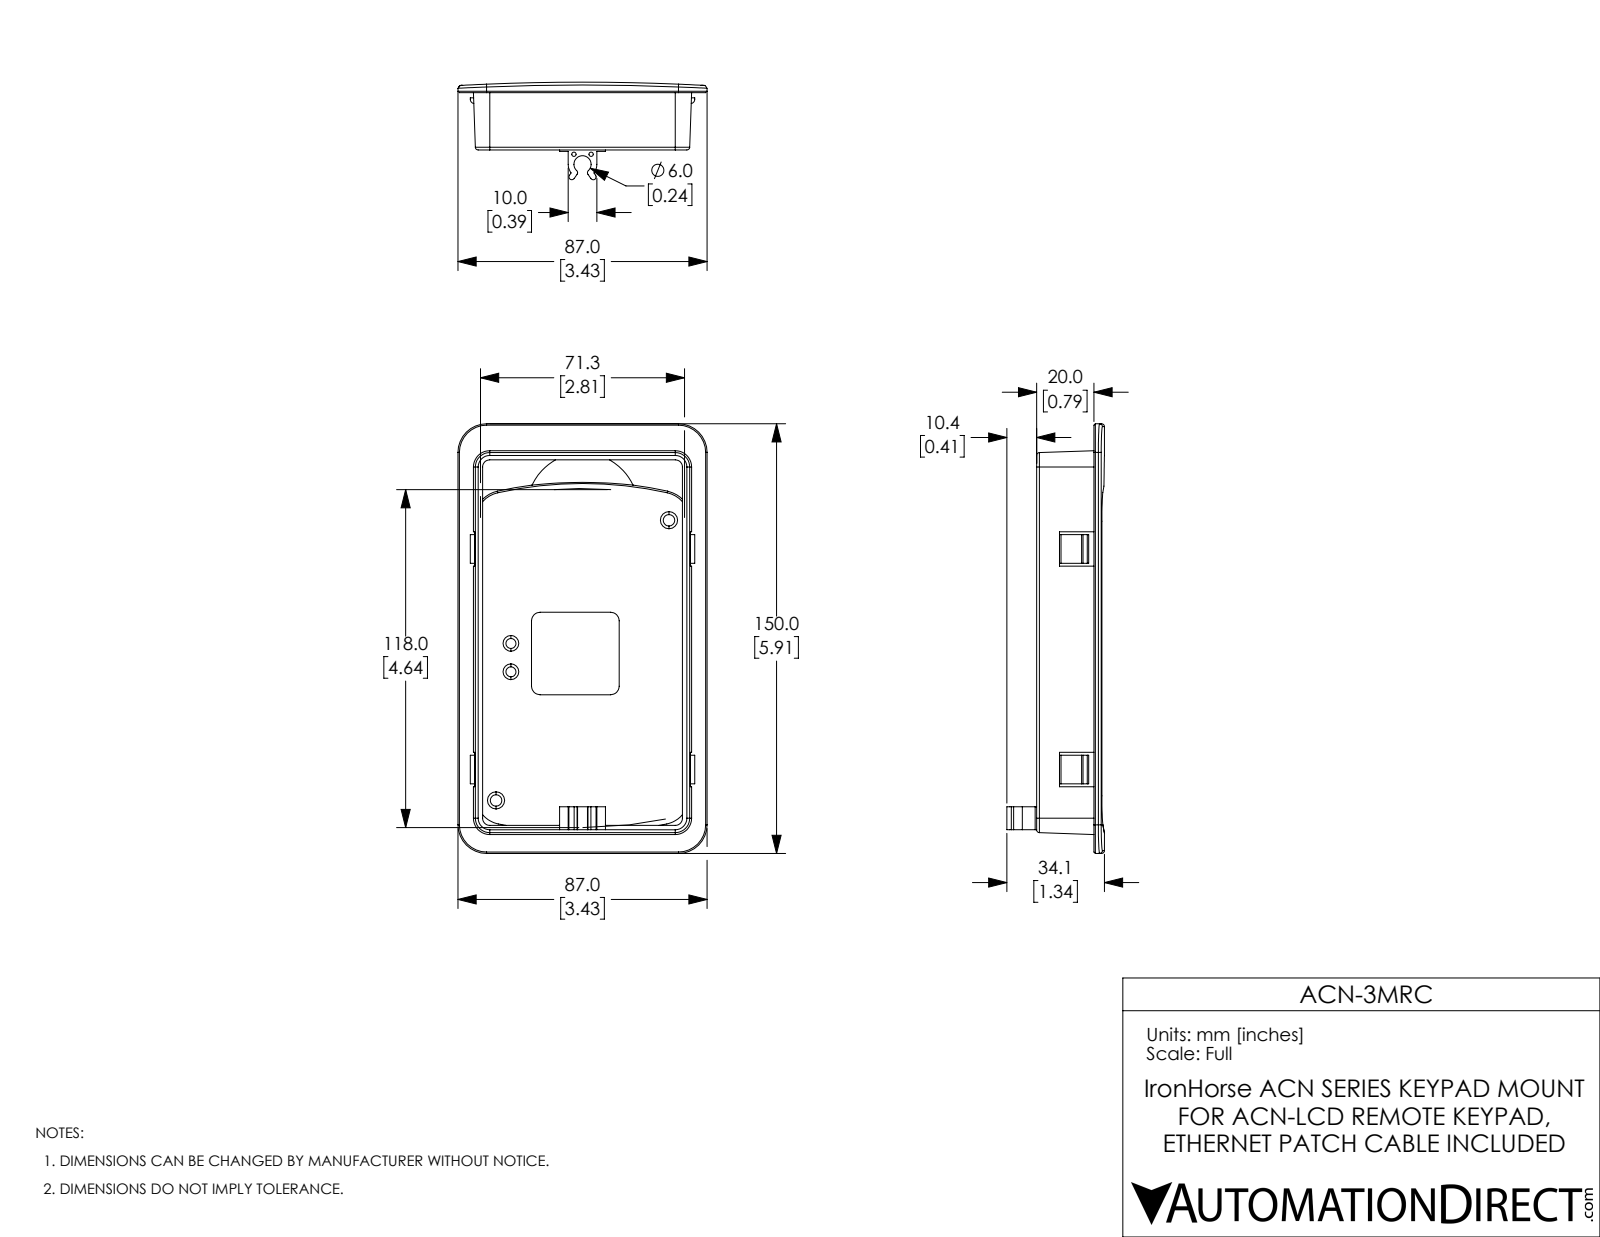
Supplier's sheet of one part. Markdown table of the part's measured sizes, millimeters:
| quantity | value |
| --- | --- |
| part name | ACN-3MRC |
| STEP written by | SolidWorks 2017 (AUTOMOTIVE_DESIGN) |
| units | millimeters |
| bodies | 1 solid, 200 faces (88 planar, 59 cylindrical, 53 other) |
| overall size | 150 × 87 × 34.6 |
| volume | 55 500 mm³ |
| surface area | 44 350 mm² |
| round holes (diameter × count) | 1.5 × 2, 3.5 × 2, 4 × 2 |
| partial cylindrical surfaces (radius × count) | 1 × 10, 0.5 × 8, 10 × 6, 3 × 5, 1.5 × 4, 2.5 × 4, 5 × 1, 145 × 1 |
| main face-to-face distances | 2.5, 1.5, 20, 1, 69.8, 71.3, 78.4, 7.1, 8.6, 79.9 |
| hole center spacings | 6, 9.9, 45.2, 55, 70, 76.5, 115 |
